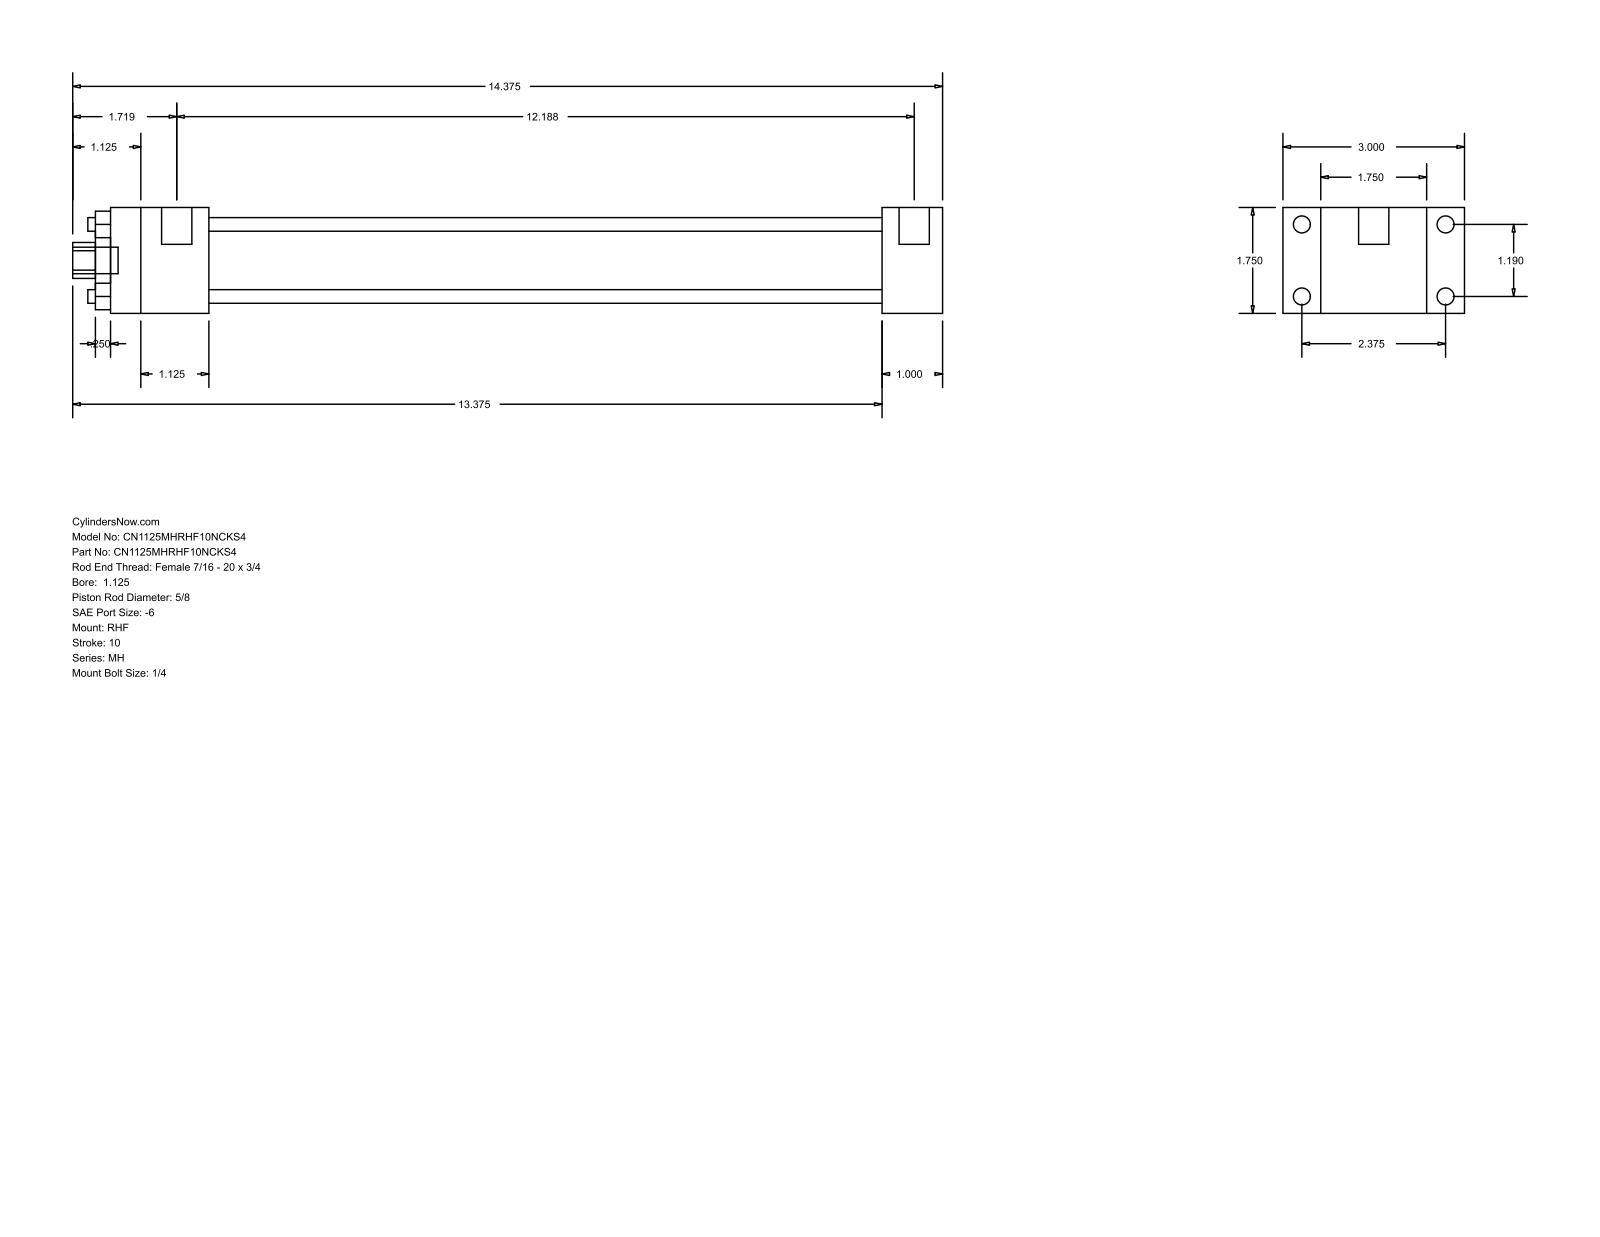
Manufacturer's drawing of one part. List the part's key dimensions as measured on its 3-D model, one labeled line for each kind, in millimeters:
Part name (STEP PRODUCT): MH_RHF__0112_0.625
STEP written by: GSSL Pune (CONFIG_CONTROL_DESIGN)
Units: millimetres
Bodies: 0 solids, 88 faces (60 planar, 28 cylindrical, 0 other)
Overall size (bounding box): 365.12 × 76.2 × 44.45
Round holes (diameter × count): ⌀5.71 ×4, ⌀15.88 ×1, ⌀28.57 ×1, ⌀34.92 ×1
Round bosses / shafts (diameter × count): ⌀7.14 ×4, ⌀5.56 ×4, ⌀12.7 ×2, ⌀11.11 ×1
Partial cylindrical surfaces — rounded edges, fillets, slot ends (radius × count): R7.54 ×1
Main face-to-face distances: 44.46, 15.87, 60.33, 25.39, 76.2, 282.58, 307.97, 41.27, 323.85, 349.24
Hole centre spacings: 21.37, 30.22, 42.74
